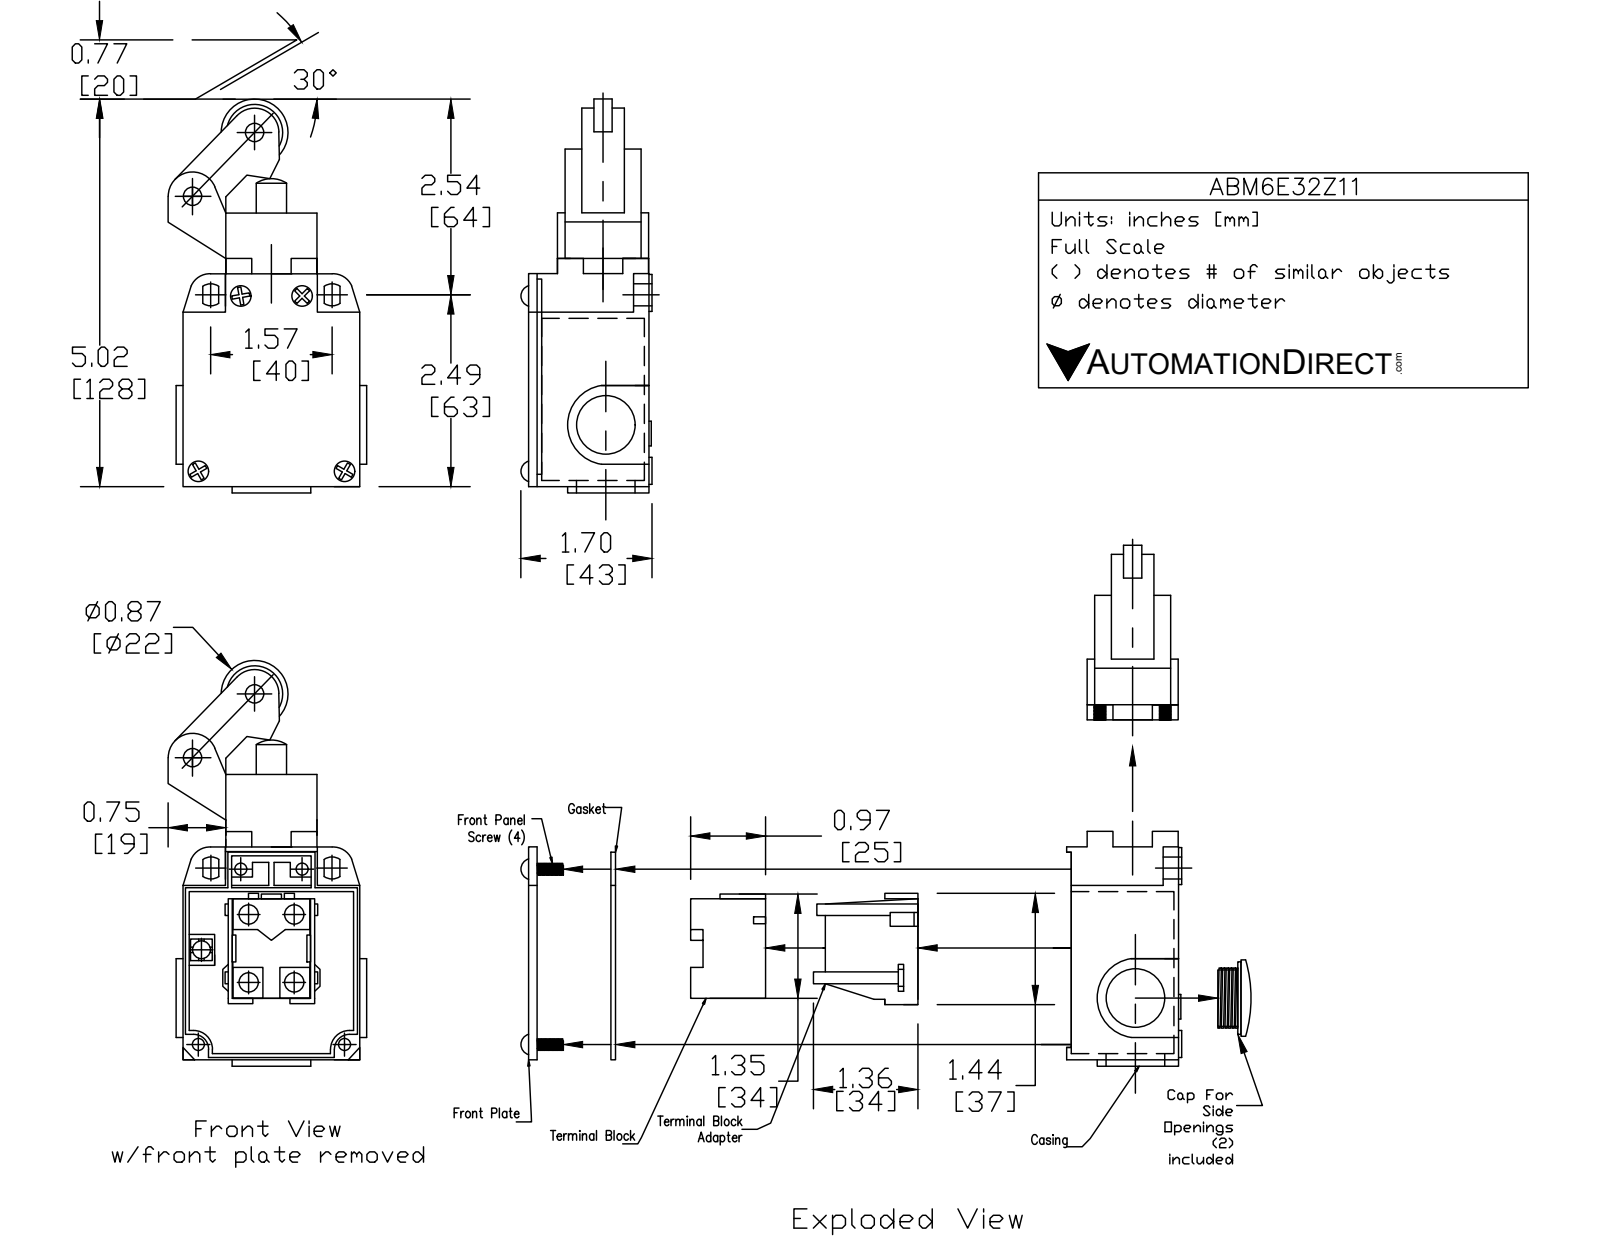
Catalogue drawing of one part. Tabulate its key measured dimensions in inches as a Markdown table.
| quantity | value |
| --- | --- |
| part name | ABM6E32Z11 |
| STEP written by | SolidWorks 2017 (AUTOMOTIVE_DESIGN) |
| units | inches |
| bodies | 4 solids, 242 faces (117 planar, 94 cylindrical, 31 other) |
| overall size | 5.11 × 2.559 × 1.705 |
| volume | 10.92 in³ |
| surface area | 53.31 in² |
| round holes (diameter × count) | 0.669 × 2, 0.748 × 2, 0.394 × 1 |
| round bosses / shafts (diameter × count) | 0.276 × 5, 0.472 × 2, 0.354 × 2, 0.866 × 1, 0.453 × 1, 0.394 × 1 |
| partial cylindrical surfaces (radius × count) | 0.059 × 12, 0.039 × 5, 0.144 × 2, 0.256 × 2, 0.315 × 2, 0.472 × 2, 0.512 × 2, 0.236 × 1 |
| main face-to-face distances | 1.555, 0.118, 0.325, 0.738, 0.551, 1.732, 0.079, 0.197, 2.283, 0.856 |
| hole center spacings | 0.039 |
